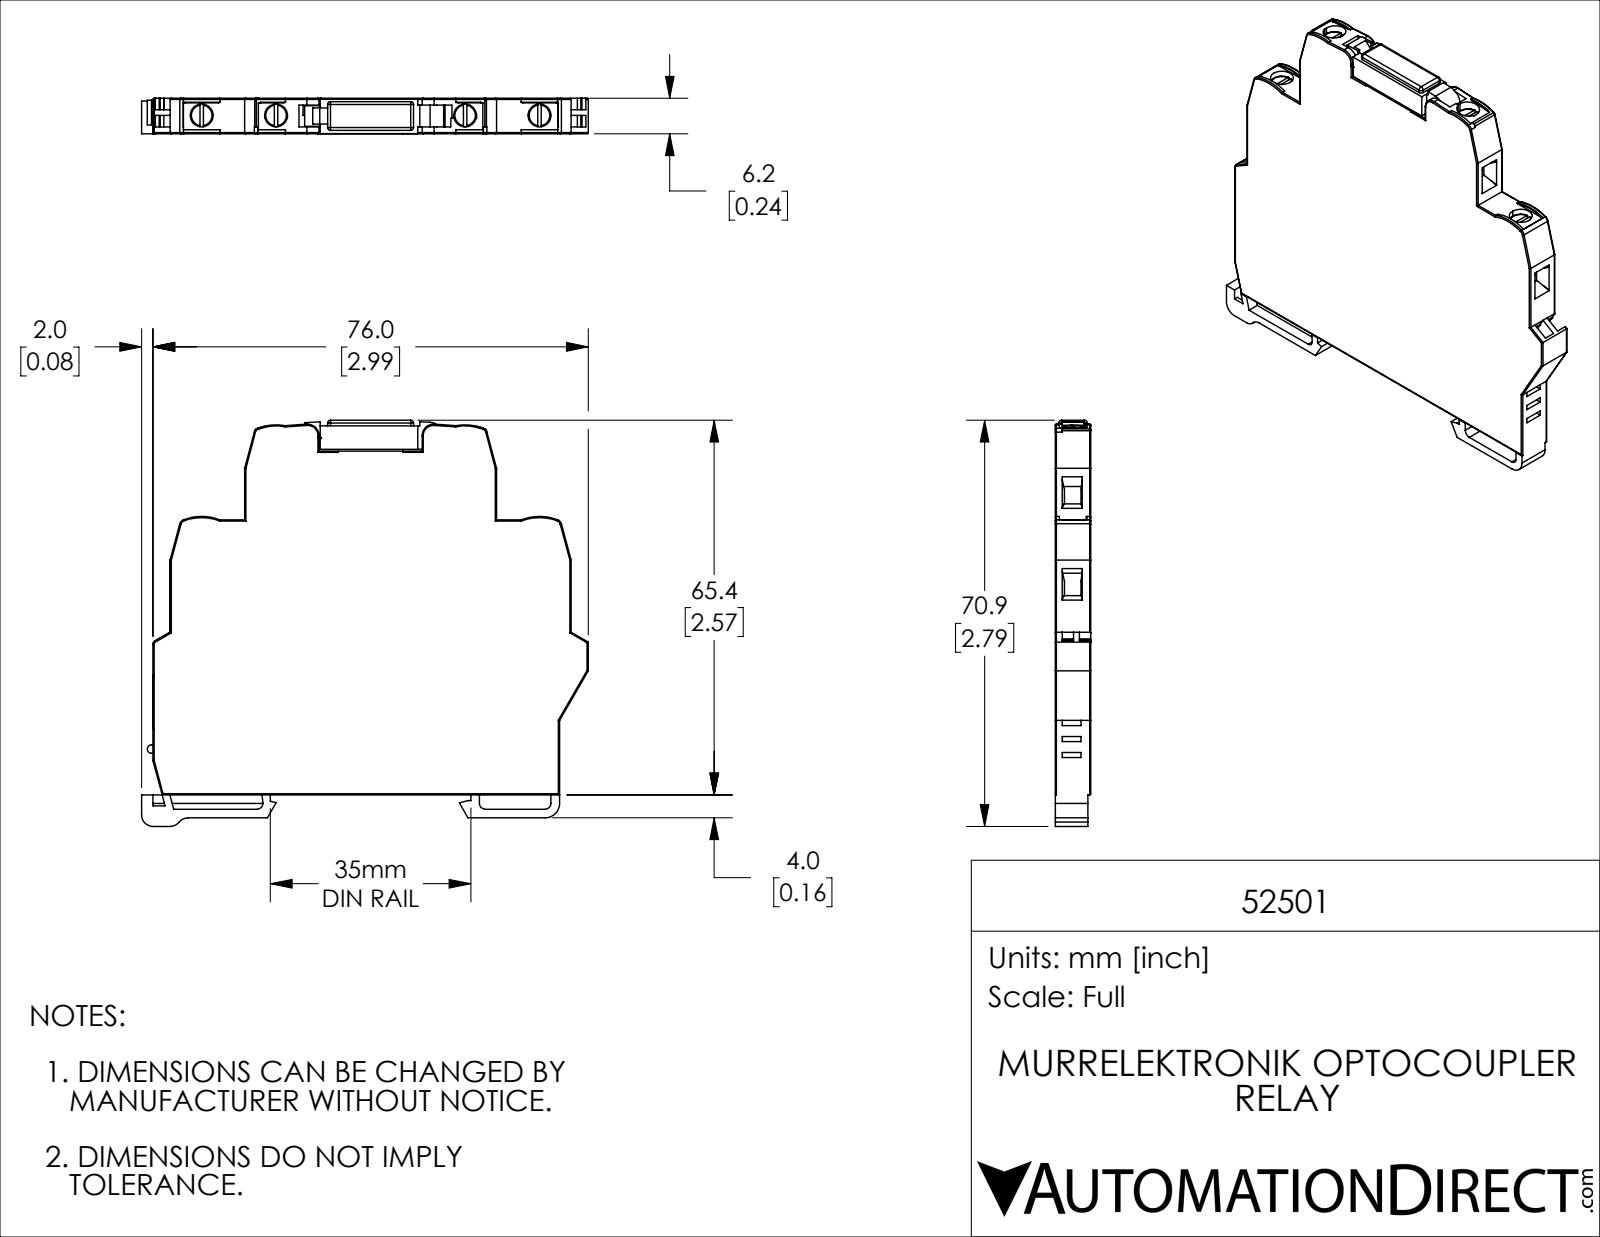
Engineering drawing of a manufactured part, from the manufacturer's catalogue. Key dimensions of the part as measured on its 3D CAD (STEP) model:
Part name (STEP PRODUCT): 52501
STEP written by: SolidWorks 2019 (CONFIG_CONTROL_DESIGN)
Units: inches
Bodies: 2 solids, 496 faces (298 planar, 138 cylindrical, 60 other)
Overall size (bounding box): 3.071 × 2.791 × 0.244
Volume: 1.561 in³ · Surface area: 18.26 in²
Round holes (diameter × count): ⌀0.157 ×4, ⌀0.075 ×1
Round bosses / shafts (diameter × count): ⌀0.079 ×1
Partial cylindrical surfaces — rounded edges, fillets, slot ends (radius × count): R0.008 ×50, R0.02 ×11, R0.039 ×7, R0.079 ×6, R0.03 ×5, R0.005 ×4, R0.346 ×4, R0.016 ×3
Main face-to-face distances: 0.244, 0.059, 0.197, 0.118, 0.098, 2.362, 0.157, 0.079, 0.047, 0.02
Hole centre spacings: 0.512, 1.811, 1.299, 2.323
